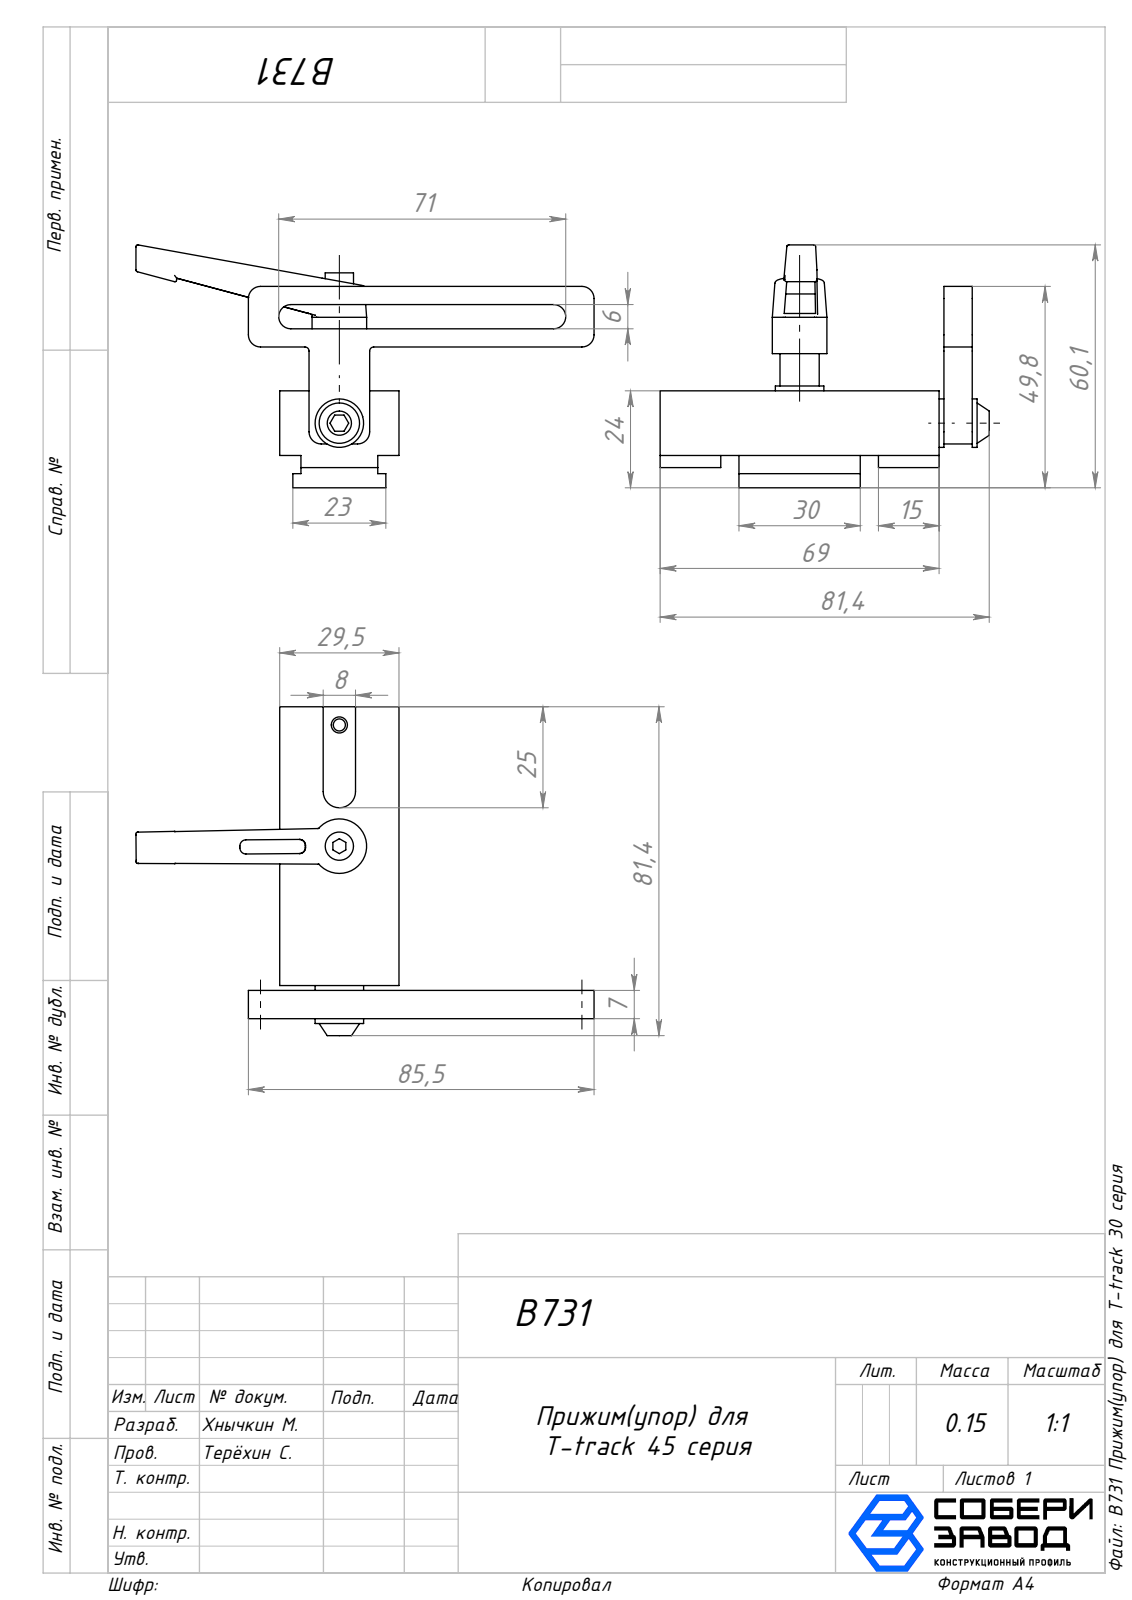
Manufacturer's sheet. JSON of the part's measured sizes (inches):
{"part_name": "B731 Прижим(упор) для T-track 45 серия; B731 Корпус_00; B731 Шайба_00; A395 Винт с рукояткой М6х25_Резьба схематическая (+3 more)", "step_written_by": "SolidWorks 2025 (AUTOMOTIVE_DESIGN)", "units": "inches", "bodies": {"solids": 8, "faces": 188, "planar": 86, "cylindrical": 47, "other": 55}, "overall_size": [4.461, 3.205, 2.367], "volume_in3": 3.12, "surface_area_in2": 32.51, "round_holes": [[0.197, 2], [0.244, 2], [0.118, 1], [0.236, 1], [0.248, 1]], "round_bosses_or_shafts": [[0.472, 2], [0.531, 1], [0.382, 1], [0.276, 1], [0.236, 1]], "partial_cylinders_radius": [[0.118, 8], [0.059, 4], [0.039, 2], [0.157, 1]], "face_to_face_distances": [0.63, 0.276, 0.177, 1.161, 0.413, 0.748, 0.315, 0.047, 0.591, 0.323], "hole_center_spacings": [1.181]}
